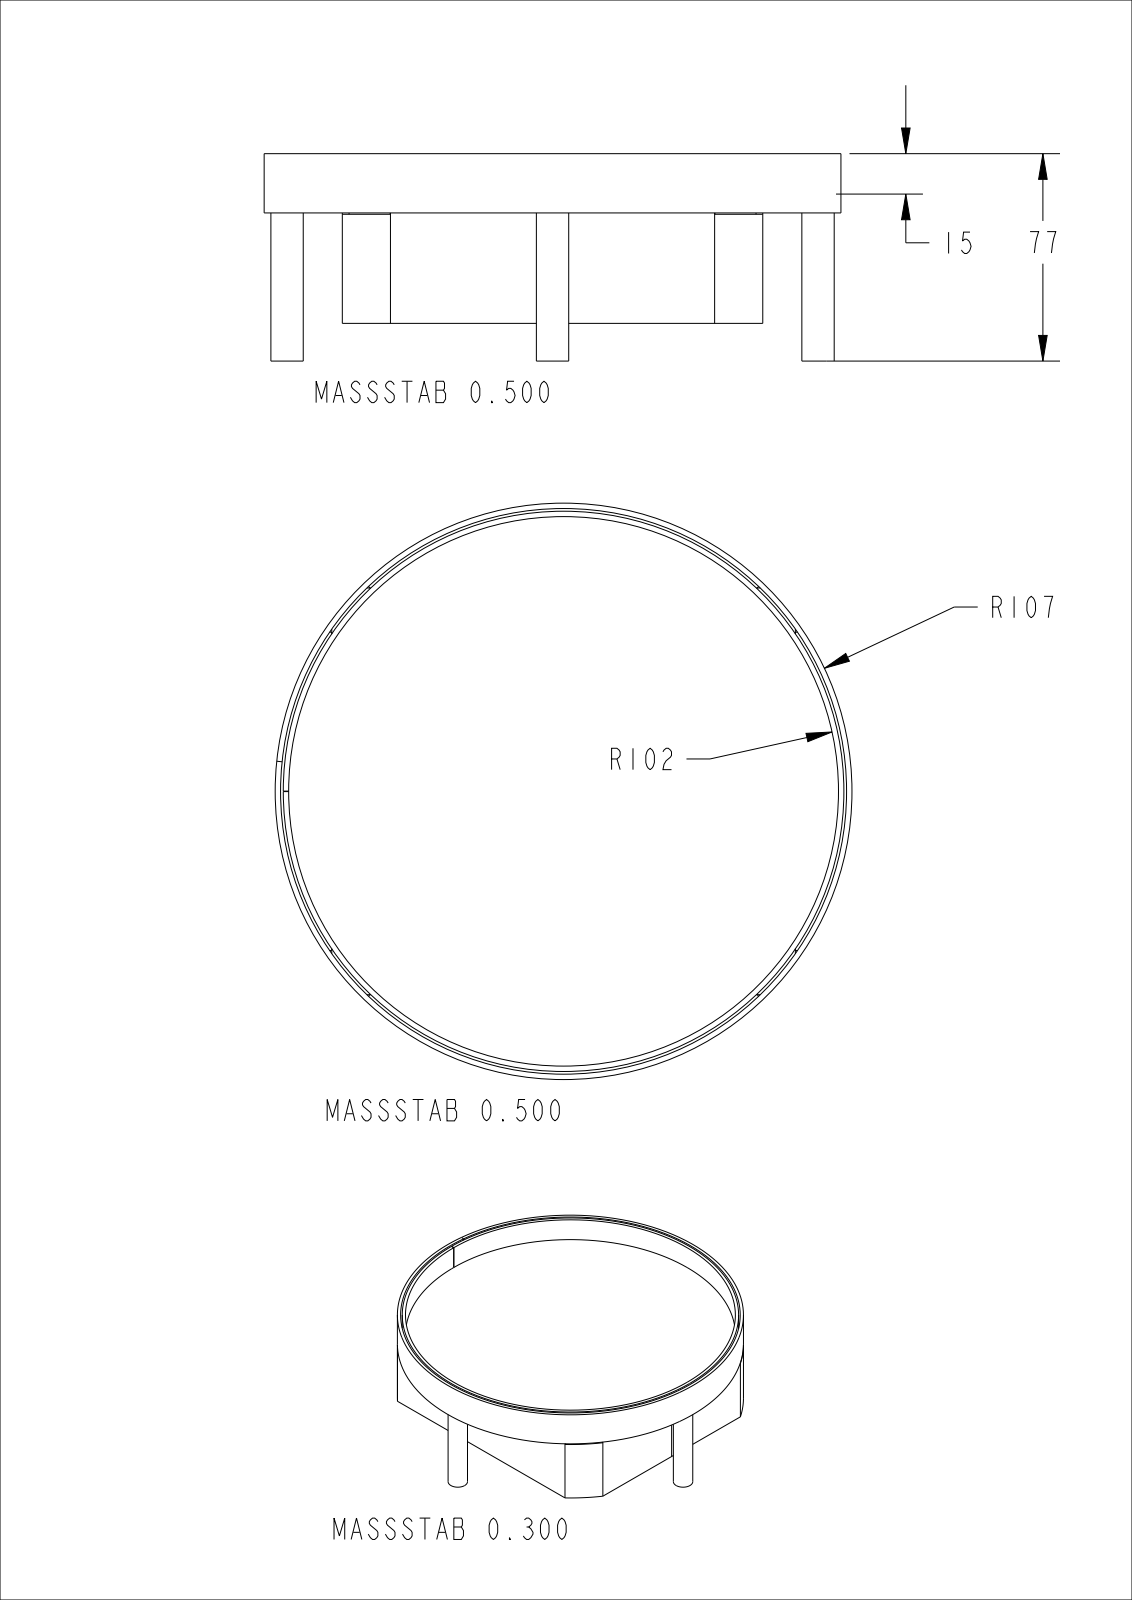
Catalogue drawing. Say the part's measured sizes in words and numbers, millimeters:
The part is named "T-00671; T-00672; T-00673; T-00674 (+8 more)". Its 3-D file was written by "CREO PARAMETRIC BY PTC INC, 2022024 (AUTOMOTIVE_DESIGN)". It is 8 solids with 155 faces: 95 planar, 60 cylindrical and 0 other. Overall it measures 214 by 214 by 77 millimeters. Its volume is 195 672 cubic millimeters and its surface area 233 730 square millimeters. Round holes: 6 of diameter 3.8, 4 of diameter 10.1, 1 of diameter 210. Round bosses or shafts: 4 of diameter 12, 4 of diameter 9.85, 1 of diameter 214, 1 of diameter 208, 1 of diameter 204. Partial cylindrical surfaces (rounded edges, fillets, slot ends): 8 of radius 0.5. The main face-to-face distances are 2, 2.5, 5, 174.5, 153.5, 7, 3, 172, 177, 151. The hole center spacings are 41.16, 97.39, 98.5, 106.34, 139.3, 164.52, 191.52, 22.01.
